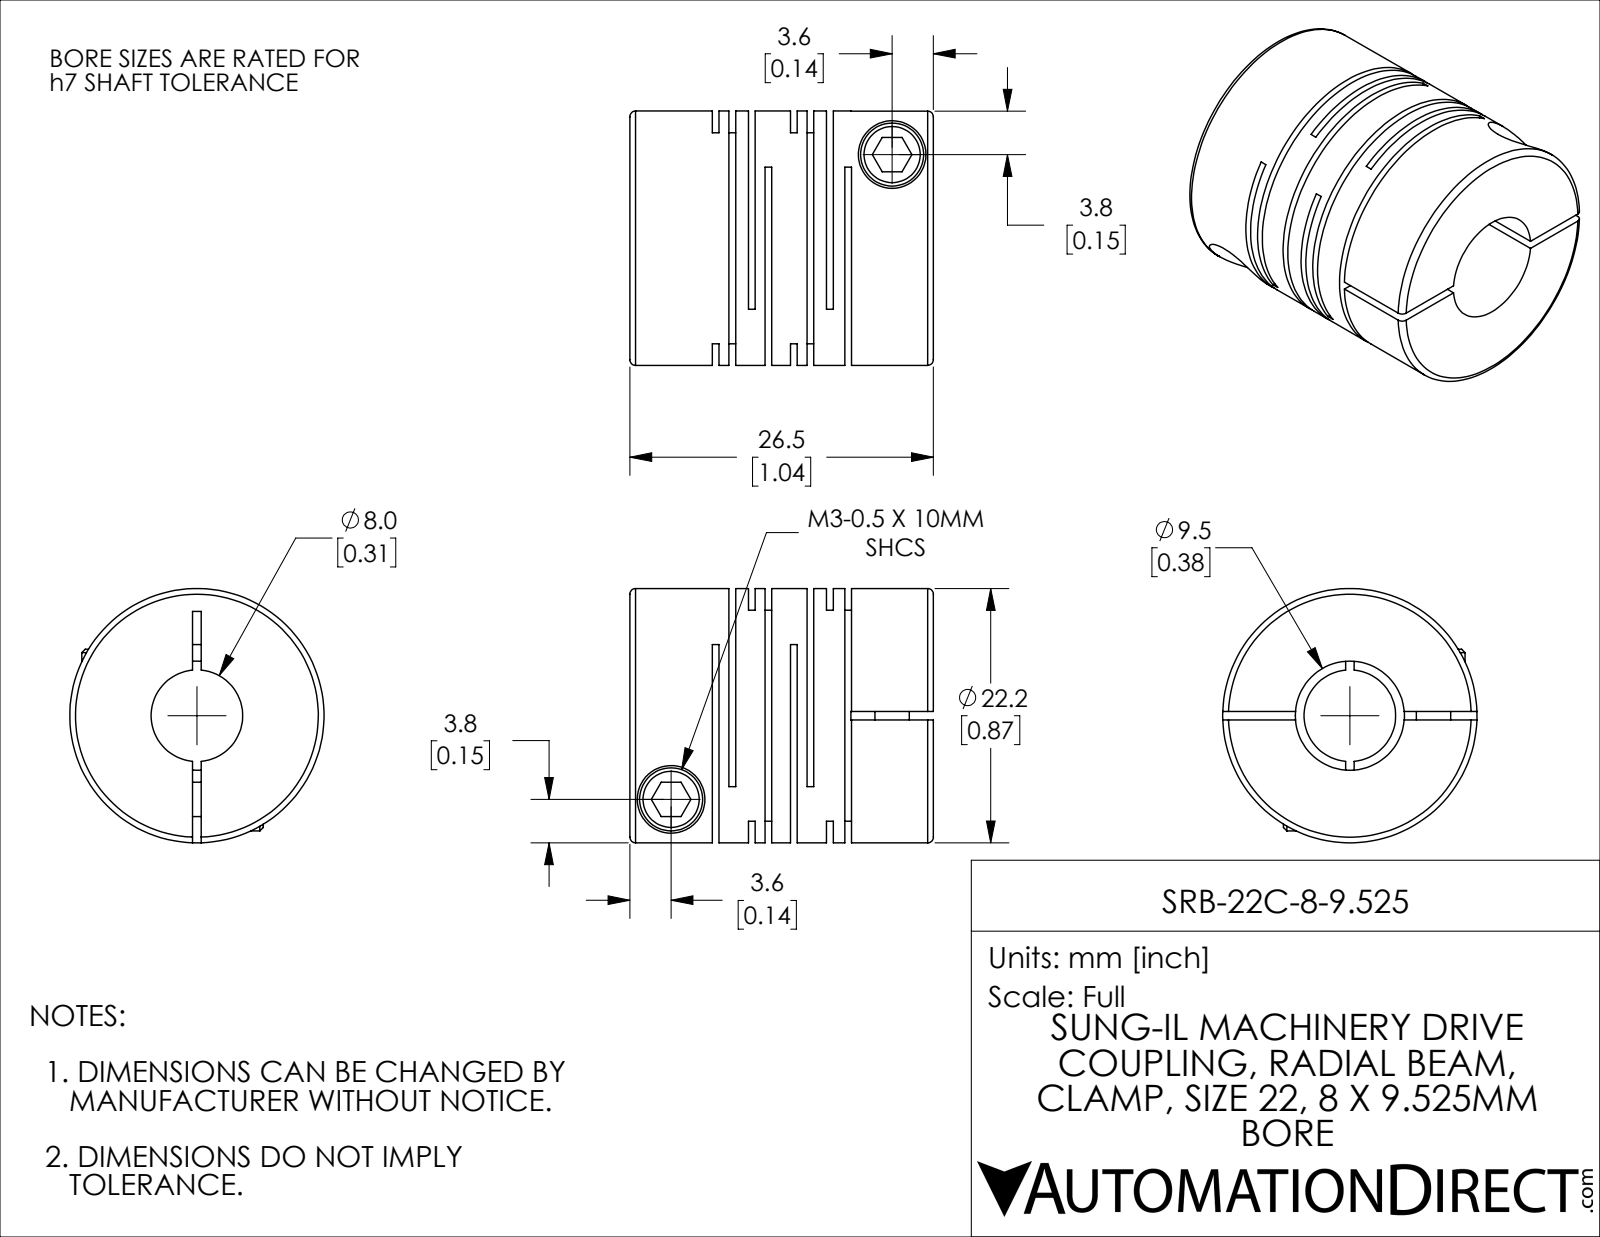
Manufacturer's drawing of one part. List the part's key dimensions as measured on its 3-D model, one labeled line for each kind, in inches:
Part name (STEP PRODUCT): SRB-22C-8-9.525
STEP written by: SolidWorks 2021 (CONFIG_CONTROL_DESIGN)
Units: inches
Bodies: 1 solid, 115 faces (60 planar, 42 cylindrical, 13 other)
Overall size (bounding box): 1.043 × 0.874 × 0.874
Volume: 0.428 in³ · Surface area: 11.74 in²
Round holes (diameter × count): ⌀0.118 ×2, ⌀0.232 ×2, ⌀0.315 ×1, ⌀0.375 ×1
Round bosses / shafts (diameter × count): ⌀0.217 ×2, ⌀0.874 ×1
Main face-to-face distances: 0.023, 0.269, 0.057, 0.124, 0.211, 0.144, 0.067, 0.292, 0.245, 0.08
